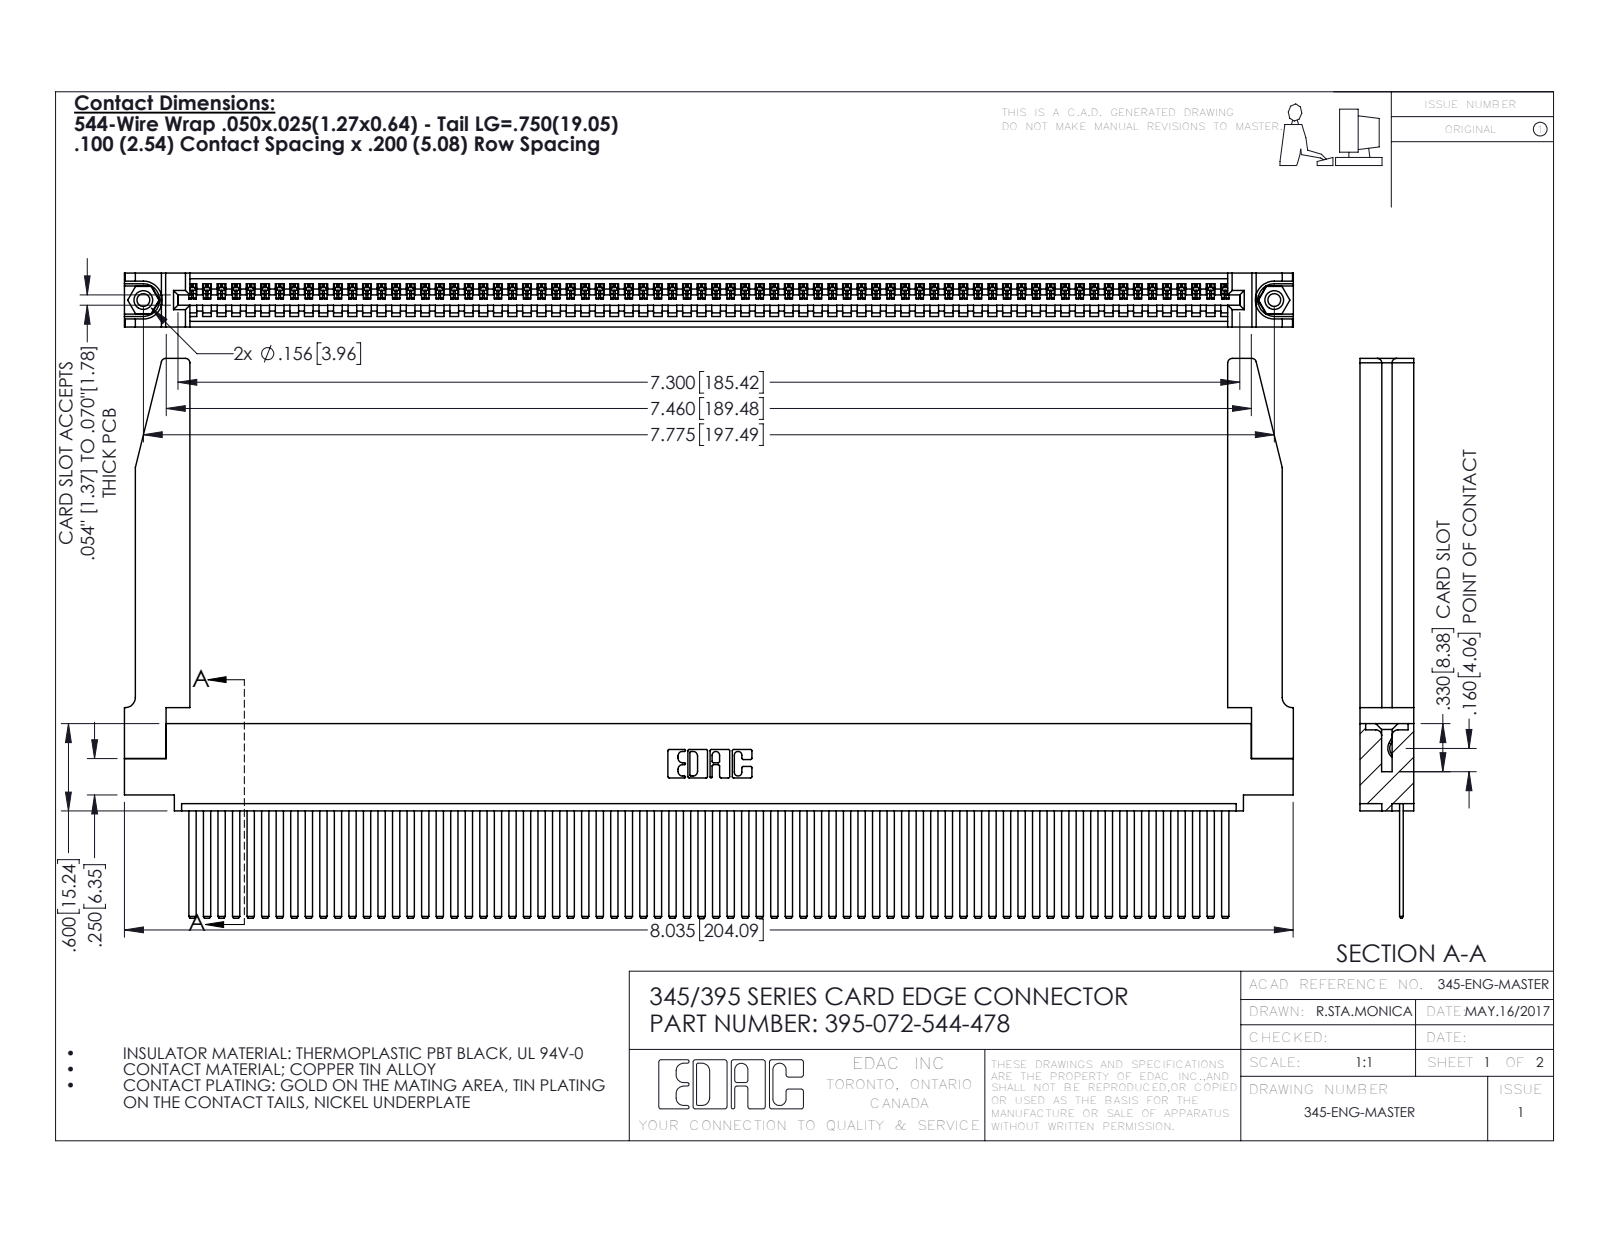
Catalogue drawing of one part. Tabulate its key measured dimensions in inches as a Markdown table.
| quantity | value |
| --- | --- |
| part name | 395-072-544-478; 345-250-001_345-250-001-102; 345-220-078_345-220-078; 345-292-001_345-293-144 (+1 more) |
| STEP written by | SolidWorks 2016 (CONFIG_CONTROL_DESIGN) |
| units | inches |
| bodies | 77 solids, 4108 faces (2818 planar, 1238 cylindrical, 52 other) |
| overall size | 8.036 × 3.847 × 0.37 |
| volume | 1.719 in³ |
| surface area | 57.26 in² |
| round holes (diameter × count) | 0.089 × 2, 0.125 × 2, 0.156 × 2, 0.064 × 1 |
| round bosses / shafts (diameter × count) | 0.155 × 2 |
| partial cylindrical surfaces (radius × count) | 0.006 × 144, 0.01 × 22, 0.03 × 8, 0.007 × 6, 0.031 × 6, 0.026 × 3, 0.031 × 2, 0.04 × 2 |
| main face-to-face distances | 0.072, 0.298, 0.37, 0.098, 0.272, 0.025, 0.2, 0.225, 0.149, 0.15 |
| hole center spacings | 0.27, 7.539, 7.775 |
